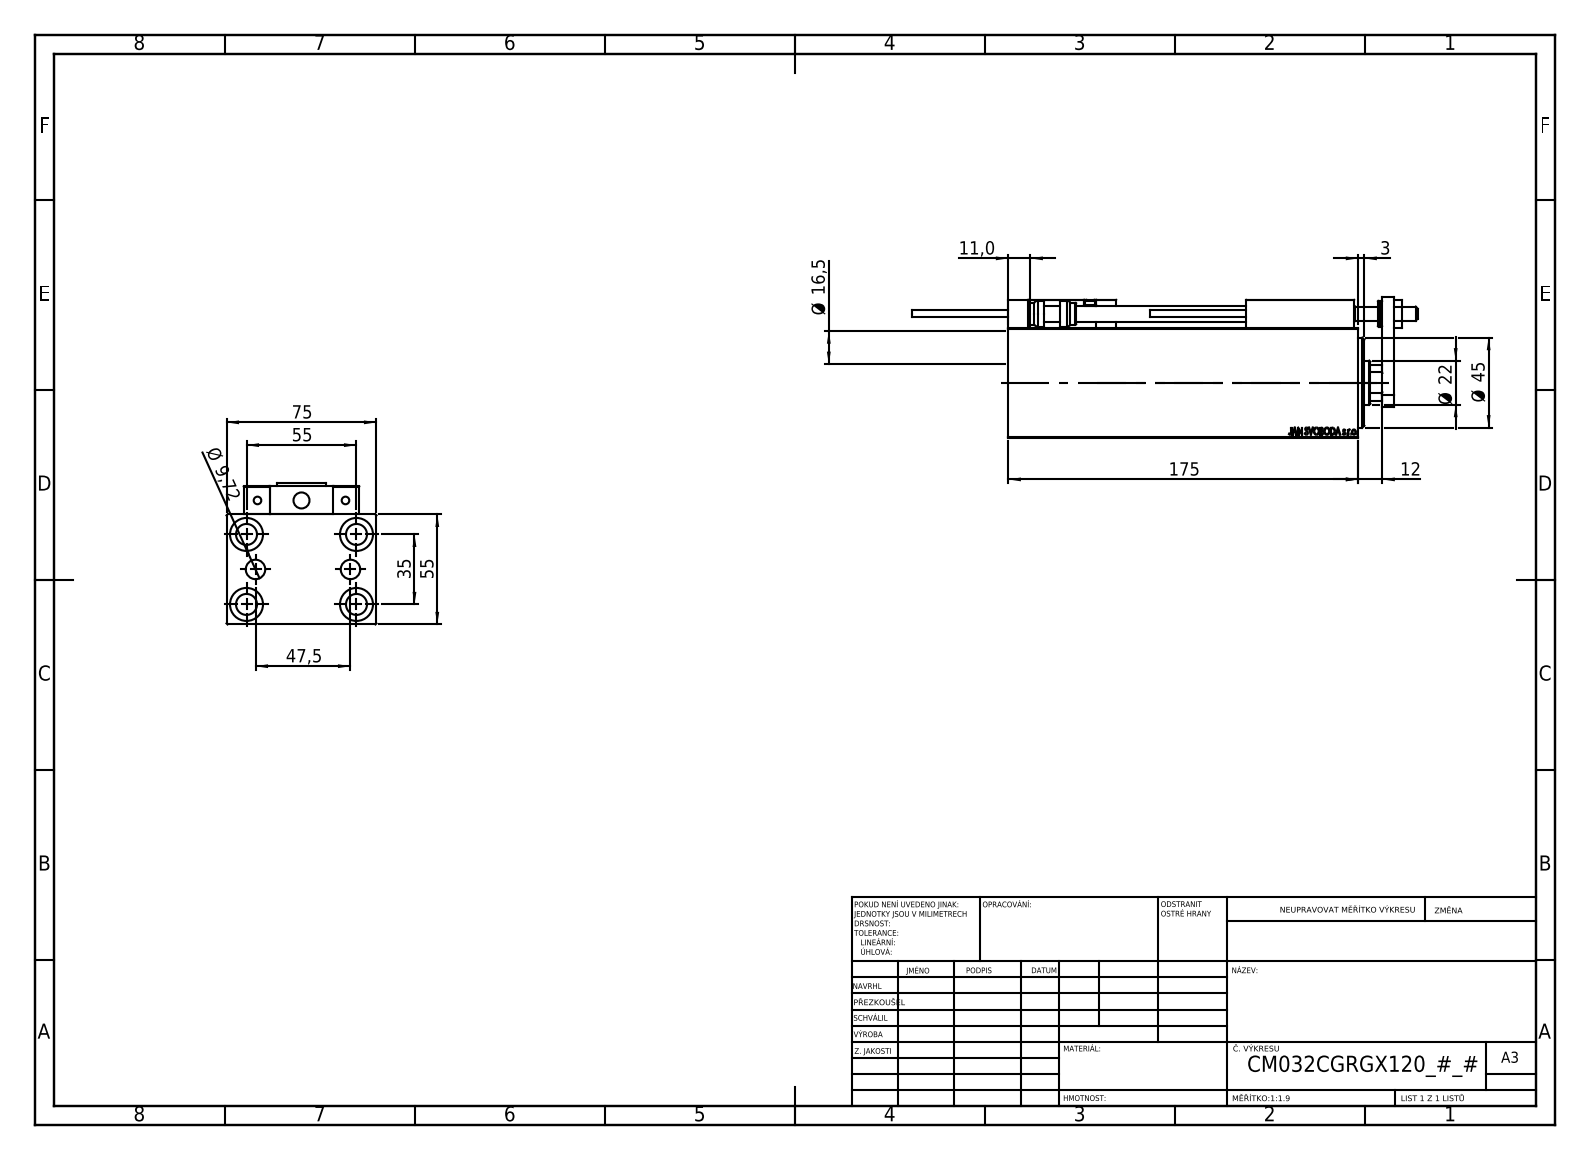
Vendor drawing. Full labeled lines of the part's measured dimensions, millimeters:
Part name (STEP PRODUCT): NUT_D12; ZARAZKA; ALLEN BOLT D8; Block (+7 more)
STEP written by: SolidWorks 2019 (CONFIG_CONTROL_DESIGN)
Units: millimetres
Bodies: 23 solids, 1272 faces (558 planar, 180 cylindrical, 534 other)
Overall size (bounding box): 252.7 × 75 × 70.5
Volume: 655 940 mm³ · Surface area: 142 420 mm²
Round holes (diameter × count): ⌀8 ×5, ⌀10.5 ×5, ⌀16.5 ×5, ⌀3.2 ×4, ⌀4 ×4, ⌀5 ×2, ⌀9.72 ×2, ⌀7 ×1, ⌀22 ×1, ⌀25.5 ×1, ⌀32 ×1, ⌀34 ×1
Round bosses / shafts (diameter × count): ⌀5 ×2, ⌀3.8 ×2, ⌀13 ×1, ⌀11 ×1
Partial cylindrical surfaces — rounded edges, fillets, slot ends (radius × count): R0.3 ×30, R3 ×2, R10.5 ×1
Main face-to-face distances: 55, 75, 14, 10, 12, 7, 69, 15, 25, 5
Hole centre spacings: 32.6, 11.37, 17.76, 18.07, 20, 29.59, 29.69, 32.33
